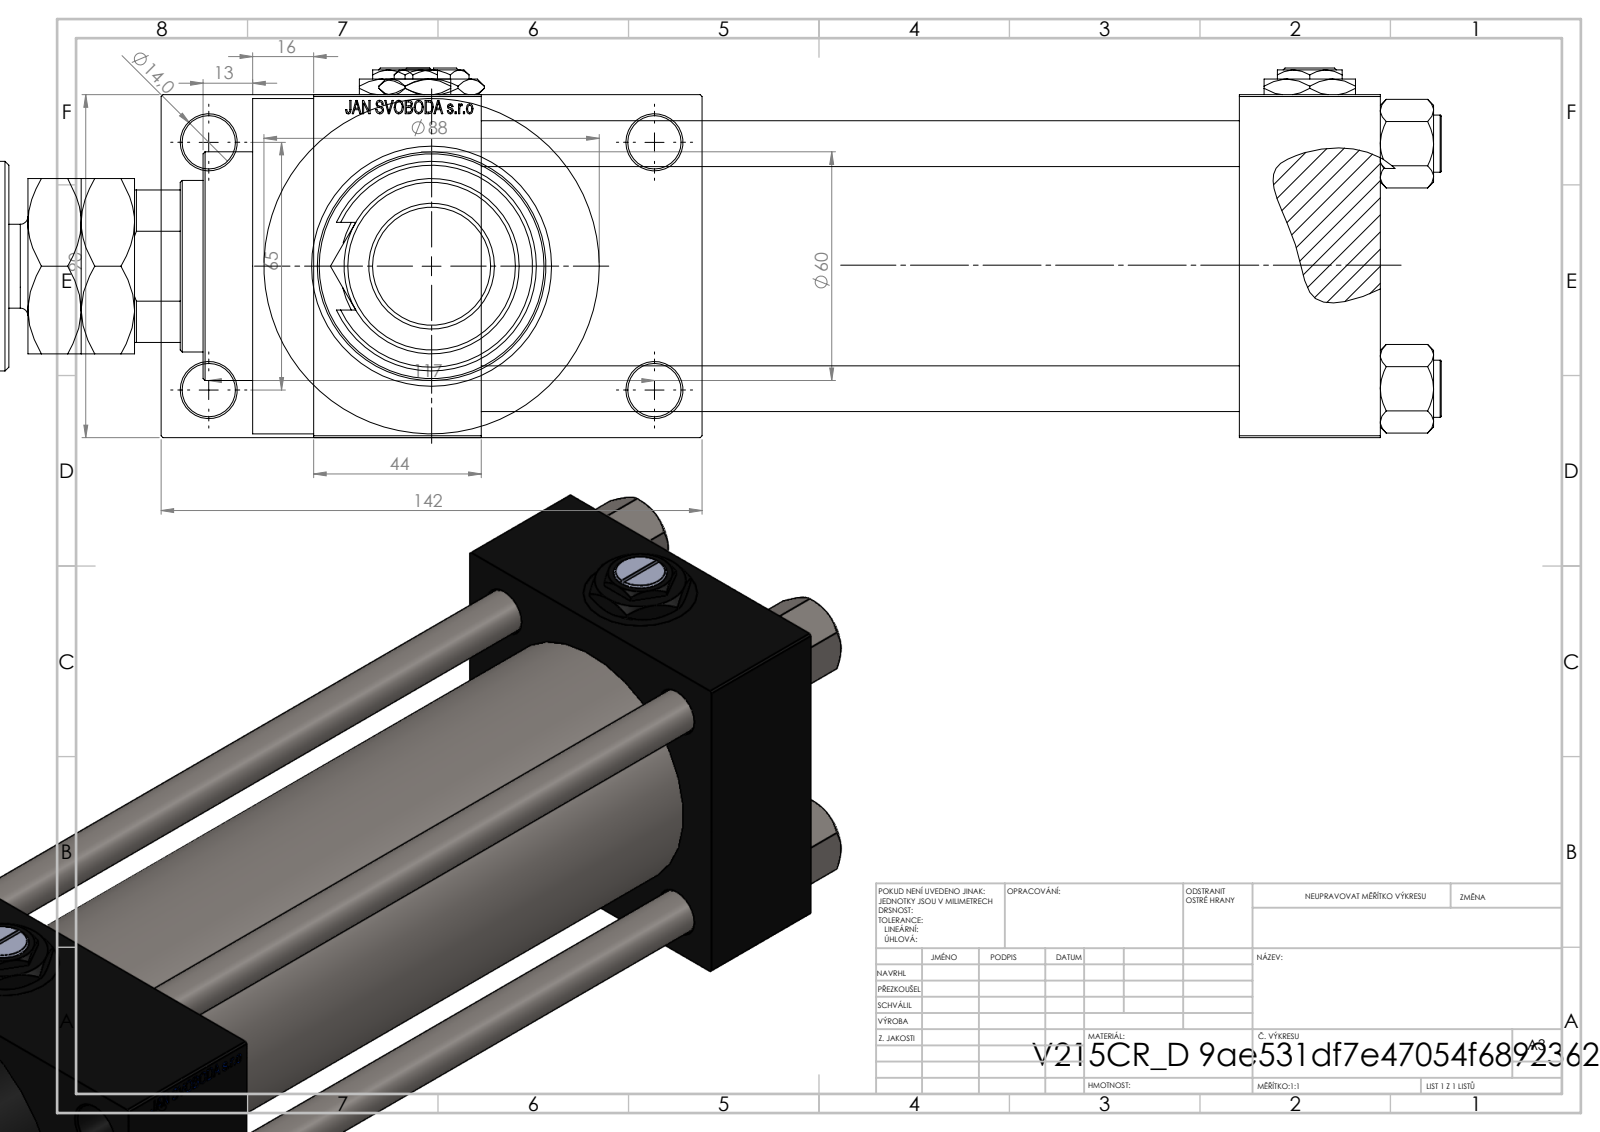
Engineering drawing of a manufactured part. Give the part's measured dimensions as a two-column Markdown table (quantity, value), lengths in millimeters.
| quantity | value |
| --- | --- |
| part name | FEMALE_PART_FOR_DFA; Zatka_pro_OIL_PORT; V215CR_D_Body; V215CR_D_TYCINKA (+4 more) |
| STEP written by | SolidWorks 2019 (CONFIG_CONTROL_DESIGN) |
| units | millimeters |
| bodies | 11 solids, 258 faces (74 planar, 44 cylindrical, 140 other) |
| overall size | 403 × 87.54 × 84.43 |
| volume | 748 510 mm³ |
| surface area | 136 740 mm² |
| round holes (diameter × count) | 12 × 4, 31.5 × 1, 45 × 1, 48 × 1 |
| round bosses / shafts (diameter × count) | 15 × 4, 63 × 1, 60 × 1, 35 × 1, 22 × 1 |
| partial cylindrical surfaces (radius × count) | 22 × 1 |
| main face-to-face distances | 46, 290, 39, 251, 60, 78, 16, 215.74, 176.74, 74.26 |
| hole center spacings | 45.47, 64.3, 90.93 |
